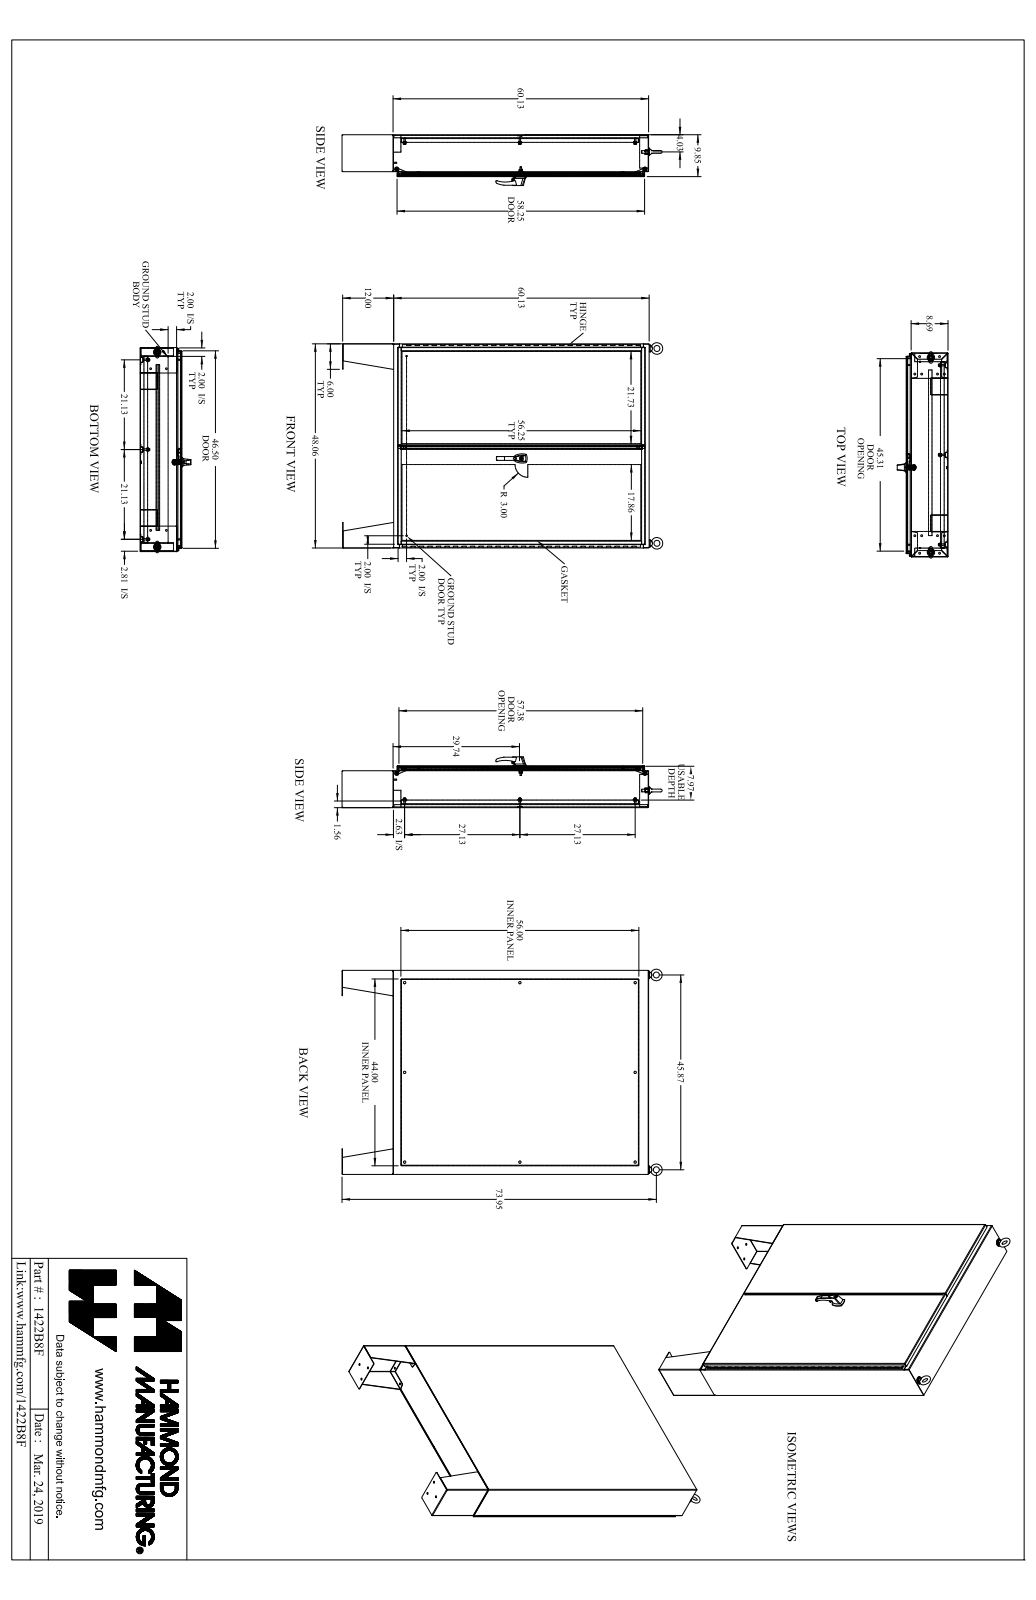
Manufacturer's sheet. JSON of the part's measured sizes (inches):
{"part_name": "1422B8F_Default", "step_written_by": "SolidWorks 2019 (CONFIG_CONTROL_DESIGN)", "units": "inches", "bodies": {"solids": 88, "faces": 2749, "planar": 1272, "cylindrical": 1230, "other": 247}, "overall_size": [75.778, 49.121, 11.963], "volume_in3": 1312, "surface_area_in2": 25972, "round_holes": [[0.304, 20], [0.437, 14], [0.307, 9], [0.563, 8], [0.445, 6], [0.11, 2], [0.25, 2], [0.257, 2], [0.28, 2], [0.281, 2], [0.313, 2], [0.39, 2]], "round_bosses_or_shafts": [[1, 10], [0.65, 8], [0.375, 8], [0.33, 8], [0.281, 4], [0.25, 4], [1.75, 2], [1.5, 2]], "partial_cylinders_radius": [[0.048, 34], [0.143, 34], [0.125, 22], [0.018, 16], [0.06, 14], [0.116, 12], [0.05, 8], [0.185, 8]], "face_to_face_distances": [0.095, 9.752, 9.657, 9.847, 0.125, 8.065, 7.97, 1.687, 1.782, 8.191], "hole_center_spacings": [6, 46.778, 12, 47.919, 18, 49.762, 24, 52.232]}
